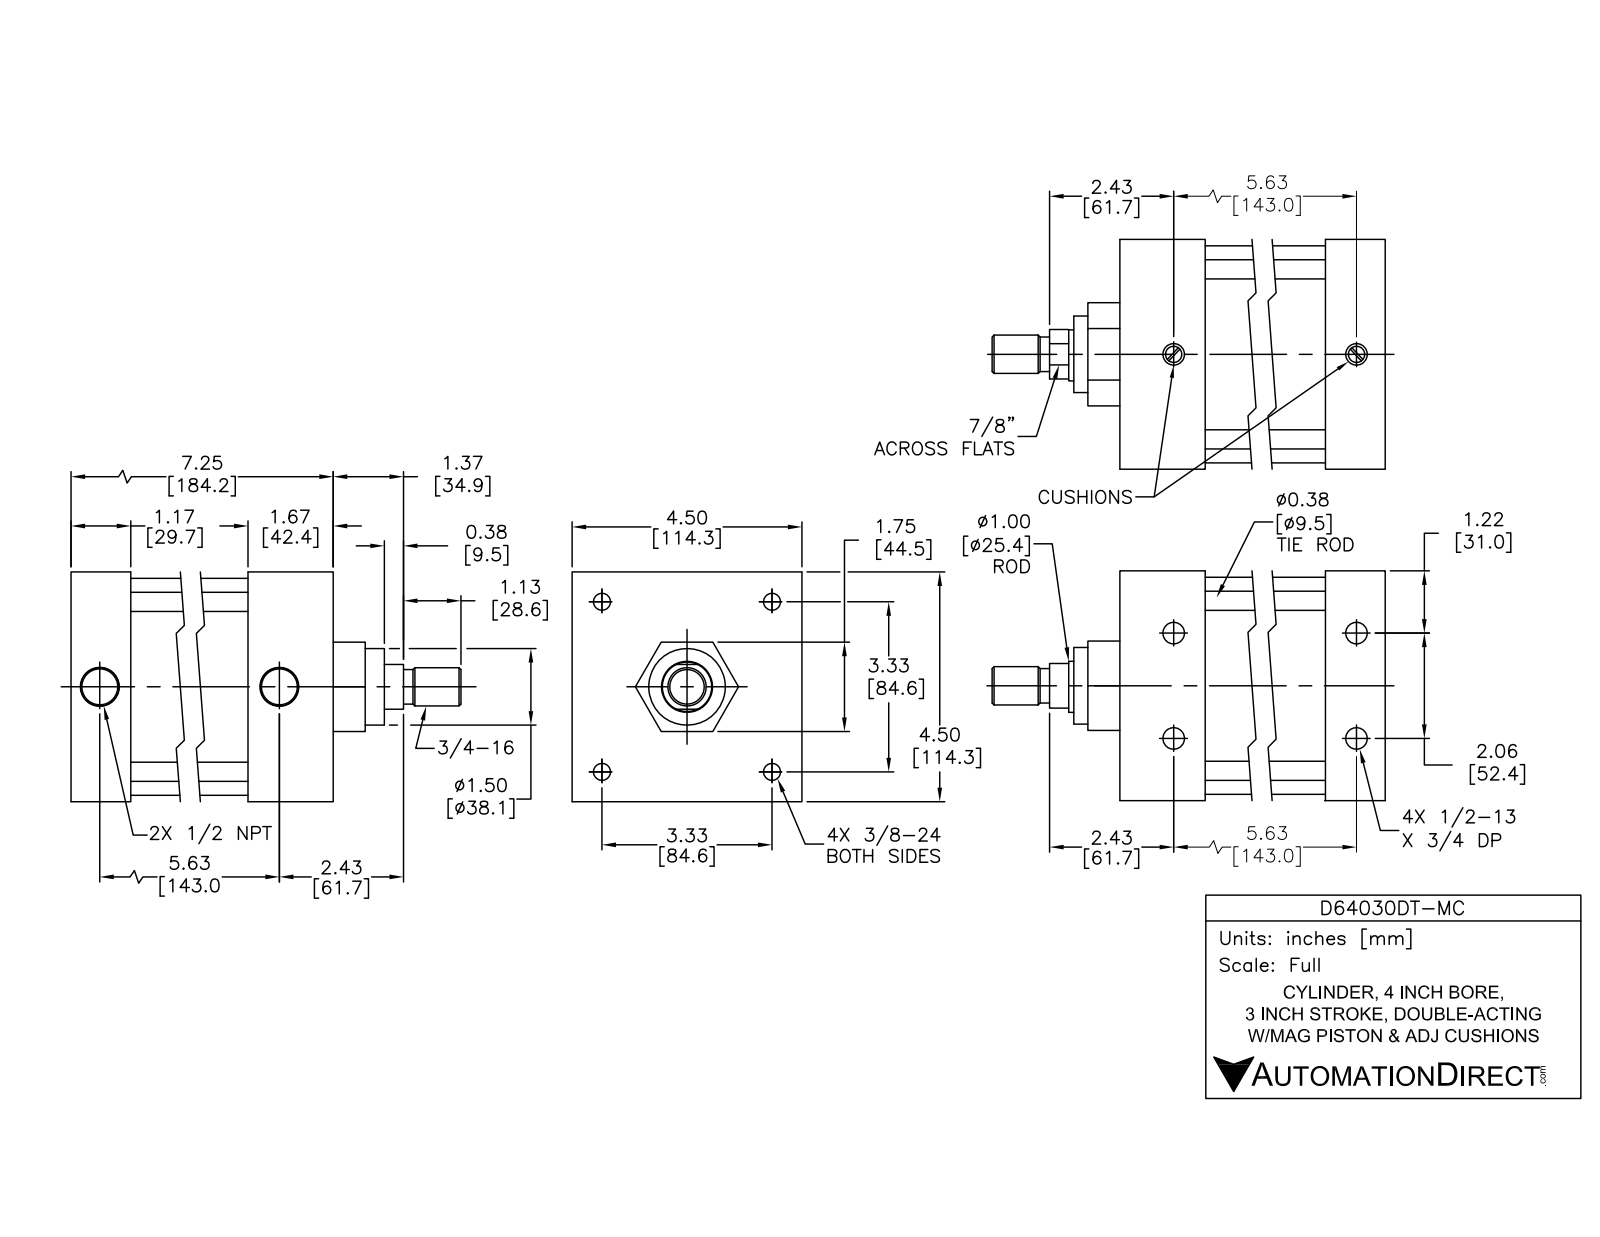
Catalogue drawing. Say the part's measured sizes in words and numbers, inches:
The part is named "D64030DT-M PISTON; D64030DT-MC; D64030DT-M BODY". Its 3-D file was written by "SolidWorks 2015 (AUTOMOTIVE_DESIGN)". It is 12 solids with 303 faces: 99 planar, 114 cylindrical and 90 other. Overall it measures 9.745 by 4.5 by 4.5 inches. Its volume is 85.63 cubic inches and its surface area 390.3 square inches. Round holes: 4 of diameter 0.33, 4 of diameter 0.406, 4 of diameter 0.417, 4 of diameter 0.625, 2 of diameter 0.5, 2 of diameter 0.766, 1 of diameter 1, 1 of diameter 1.003, 1 of diameter 4. Round bosses or shafts: 4 of diameter 0.609, 4 of diameter 0.375, 4 of diameter 0.34, 1 of diameter 4.25, 1 of diameter 3.997, 1 of diameter 1.75, 1 of diameter 0.997, 1 of diameter 0.97. Partial cylindrical surfaces (rounded edges, fillets, slot ends): 4 of radius 0.45. The main face-to-face distances are 4.5, 0.08, 4.326, 7.246, 1.75, 5.997, 1.249, 4.751, 1.246, 2.495. The hole center spacings are 1.031, 2.349, 3.322, 5.716, 5.622, 2.062, 4.698, 5.988.
